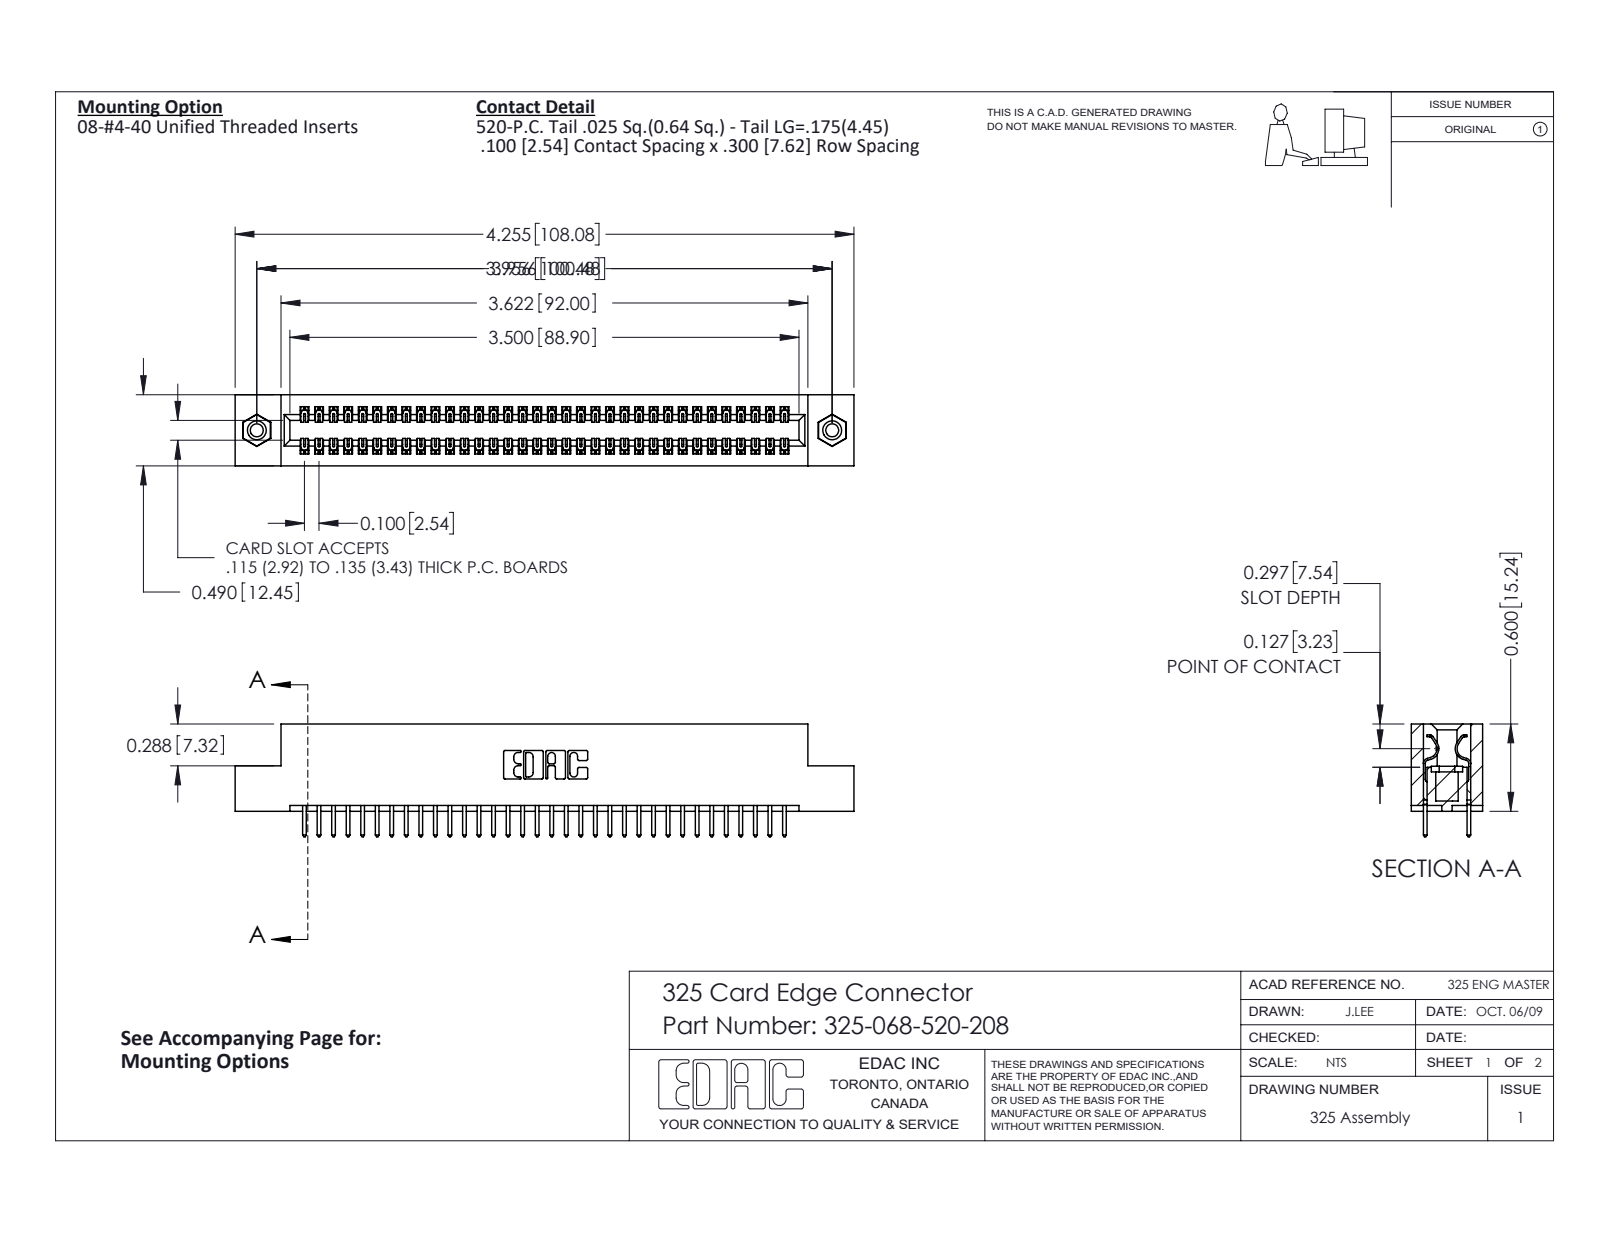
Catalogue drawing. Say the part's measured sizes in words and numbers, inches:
The part is named "325-068-520-208; 325-292-001_325-293-120; 345-250-001_345-250-003-102; 325 Part_TI". Its 3-D file was written by "SolidWorks 2016 (CONFIG_CONTROL_DESIGN)". It is 71 solids with 3710 faces: 2550 planar, 1144 cylindrical and 16 other. Overall it measures 4.255 by 0.775 by 0.49 inches. Its volume is 0.846 cubic inches and its surface area 25.52 square inches. Round holes: 2 of diameter 0.089, 2 of diameter 0.125, 2 of diameter 0.16. Round bosses or shafts: 2 of diameter 0.155. Partial cylindrical surfaces (rounded edges, fillets, slot ends): 102 of radius 0.006, 68 of radius 0.01, 22 of radius 0.01, 6 of radius 0.007, 6 of radius 0.031, 3 of radius 0.026, 2 of radius 0.014, 2 of radius 0.022. The main face-to-face distances are 0.083, 0.407, 0.3, 0.49, 0.107, 0.383, 0.025, 0.325, 0.04, 0.275. The hole center spacings are 3.956.
